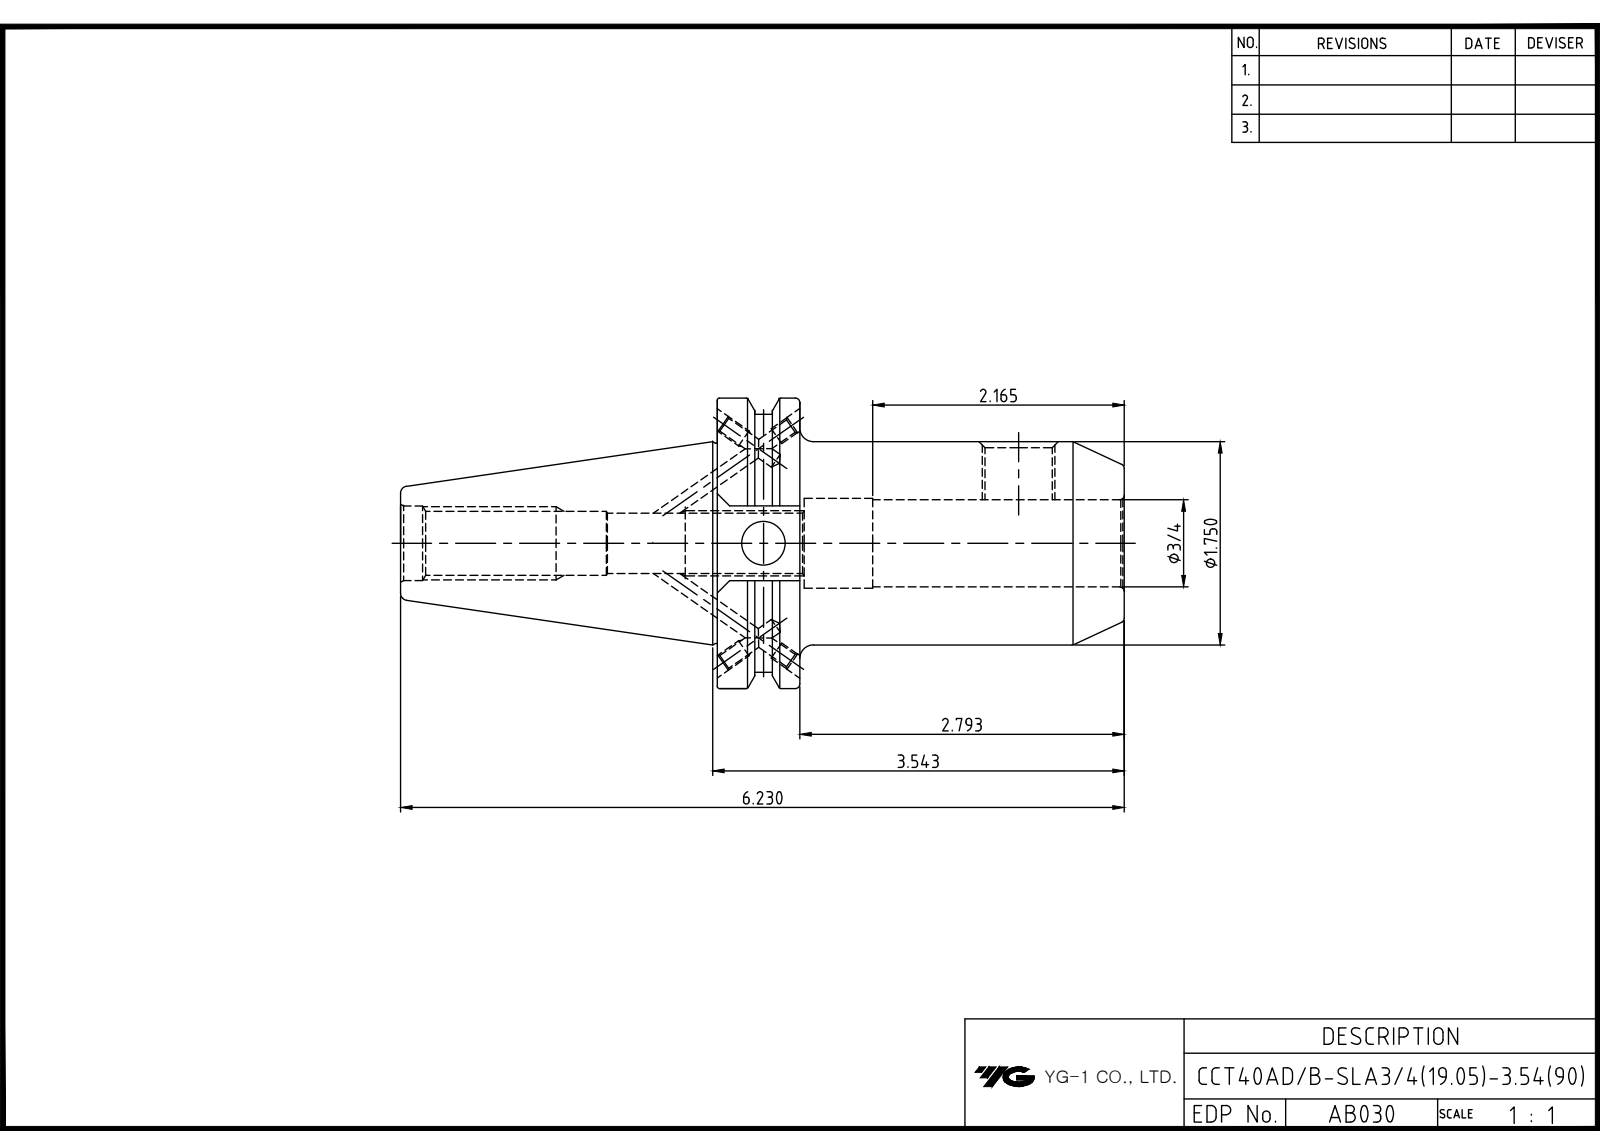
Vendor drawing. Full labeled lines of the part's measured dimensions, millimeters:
Part name (STEP PRODUCT): LO-CCT40ADB-SLA19.05-90
STEP written by: Autodesk Inventor 2025 (AUTOMOTIVE_DESIGN)
Units: millimetres
Bodies: 1 solid, 87 faces (36 planar, 27 cylindrical, 24 other)
Overall size (bounding box): 158.25 × 63.5 × 61.09
Volume: 187 695 mm³ · Surface area: 34 761 mm²
Round holes (diameter × count): ⌀3.24 ×4, ⌀4 ×4, ⌀9.53 ×1, ⌀12.57 ×1, ⌀13.39 ×1, ⌀14.35 ×1, ⌀16.3 ×1, ⌀19.05 ×1, ⌀20.25 ×1
Round bosses / shafts (diameter × count): ⌀63.5 ×1, ⌀56.3 ×1, ⌀44.45 ×1, ⌀43.8 ×1
Main face-to-face distances: 18.05, 89, 70.95, 47.6, 19, 0.95, 70, 16.38, 69.25, 87.3
Hole centre spacings: 33.88
